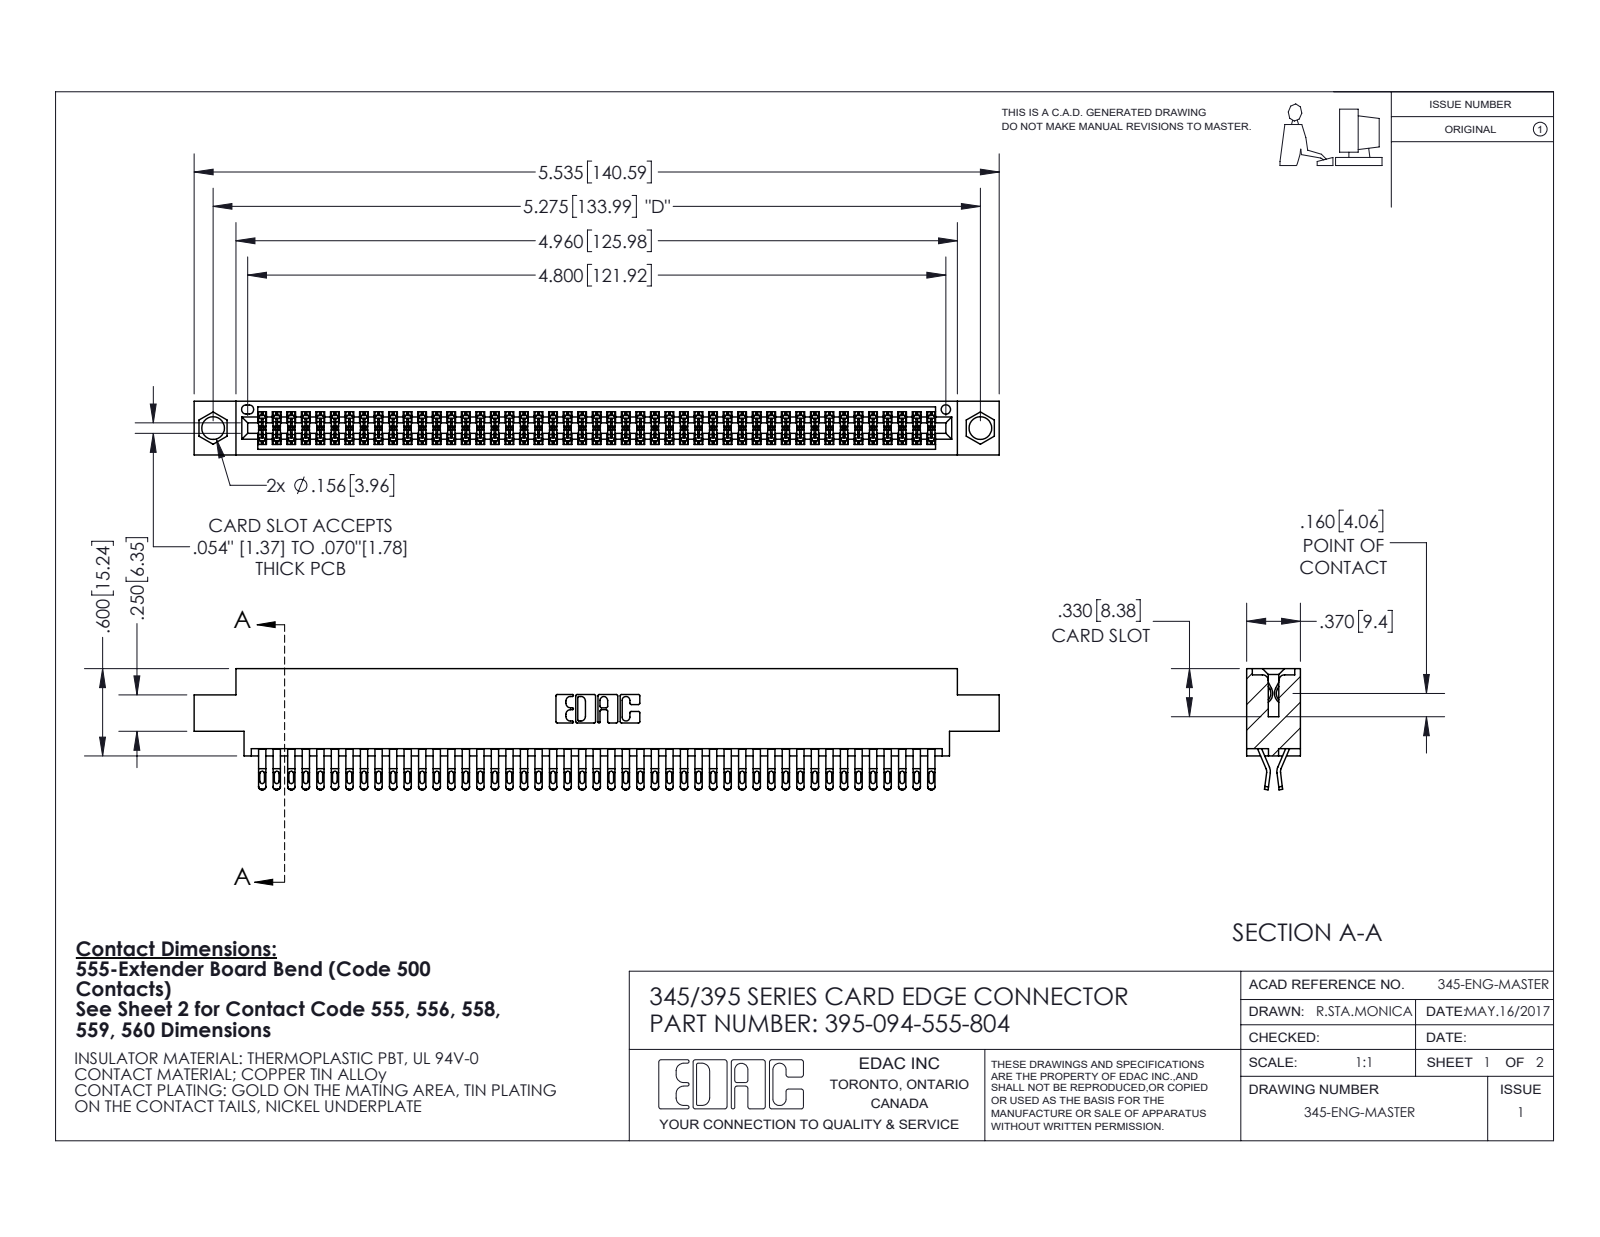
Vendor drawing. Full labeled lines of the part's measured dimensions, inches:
Part name (STEP PRODUCT): 345-292-001_555 Tail; 345 Part_0.170 Offset - 0.156 Dia-TI; 395-094-555-804
STEP written by: SolidWorks 2020 (CONFIG_CONTROL_DESIGN)
Units: inches
Bodies: 95 solids, 5408 faces (3012 planar, 2396 cylindrical, 0 other)
Overall size (bounding box): 5.535 × 0.832 × 0.37
Volume: 0.839 in³ · Surface area: 33.13 in²
Round holes (diameter × count): ⌀0.156 ×2, ⌀0.064 ×1
Partial cylindrical surfaces — rounded edges, fillets, slot ends (radius × count): R0.016 ×235, R0.006 ×188, R0.02 ×188, R0.01 ×22, R0.007 ×6, R0.031 ×6, R0.026 ×3, R0.01 ×2
Main face-to-face distances: 0.072, 0.298, 0.37, 0.025, 0.2, 0.098, 0.272, 0.225, 0.175, 0.149
Hole centre spacings: 0.27, 5.039, 5.275
